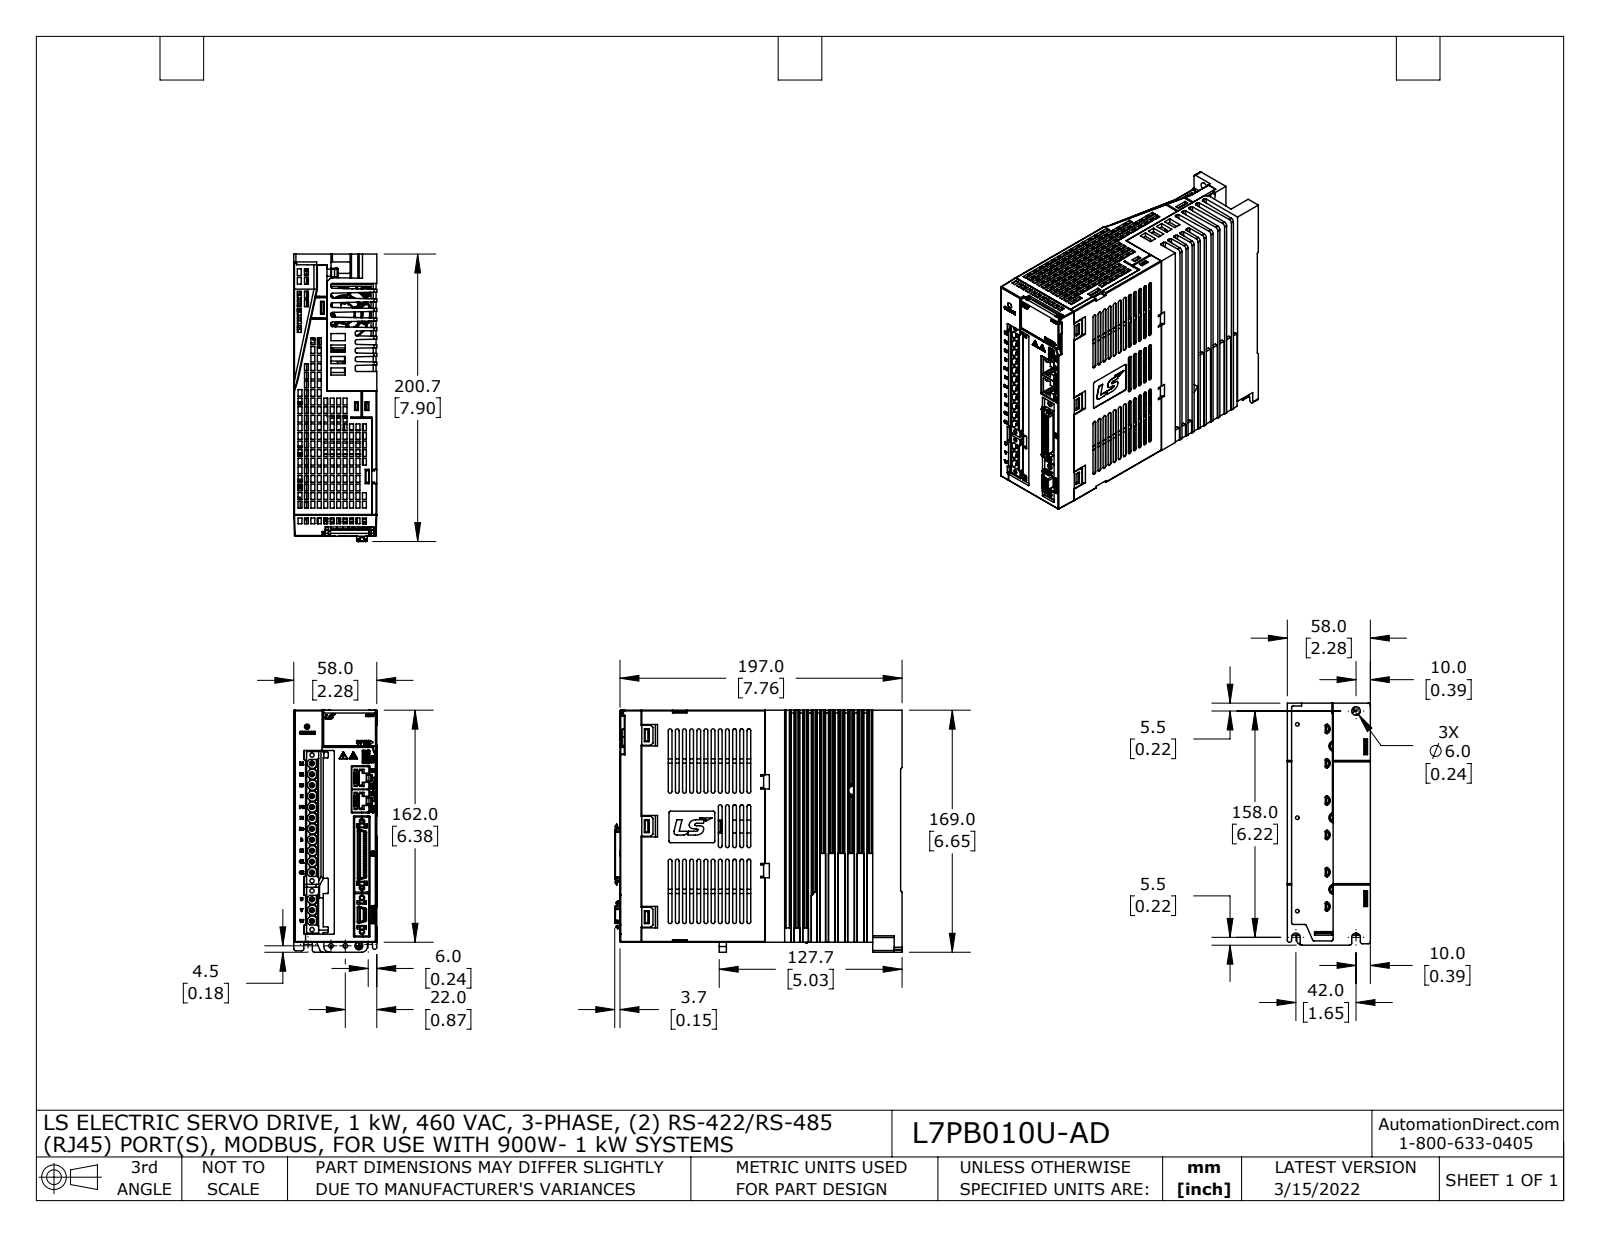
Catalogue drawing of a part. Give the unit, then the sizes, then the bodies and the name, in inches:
Units: inches
Overall size (bounding box): 8.434 × 6.654 × 2.283
Round holes (diameter × count): ⌀0.098 ×6, ⌀0.102 ×6, ⌀0.091 ×4, ⌀0.154 ×4, ⌀0.118 ×3, ⌀0.217 ×1, ⌀0.236 ×1, ⌀1.378 ×1
Round bosses / shafts (diameter × count): ⌀0.15 ×4, ⌀0.087 ×4, ⌀0.307 ×2, ⌀0.26 ×2, ⌀0.236 ×2, ⌀0.197 ×2, ⌀0.157 ×2, ⌀0.091 ×2
Partial cylindrical surfaces — rounded edges, fillets, slot ends (radius × count): R0.02 ×160, R0.039 ×38, R0.028 ×34, R0.087 ×30, R0.051 ×24, R0.008 ×14, R0.045 ×14, R0.059 ×10
Main face-to-face distances: 2.282, 0.682, 1.6, 0.683, 2.283, 1.058, 1.057, 0.375, 1.225, 6.378
Hole centre spacings: 0.238, 0.396, 0.79, 0.801, 0.931, 1.019, 1.083, 1.32
Volume: 110.3 in³ · Surface area: 342.1 in²
Bodies: 3 solids, 4252 faces (2750 planar, 803 cylindrical, 699 other)
Part name (STEP PRODUCT): L7PA010U-AD ext1b NEWbC fxt
STEP written by: SolidWorks 2021 (AUTOMOTIVE_DESIGN)
